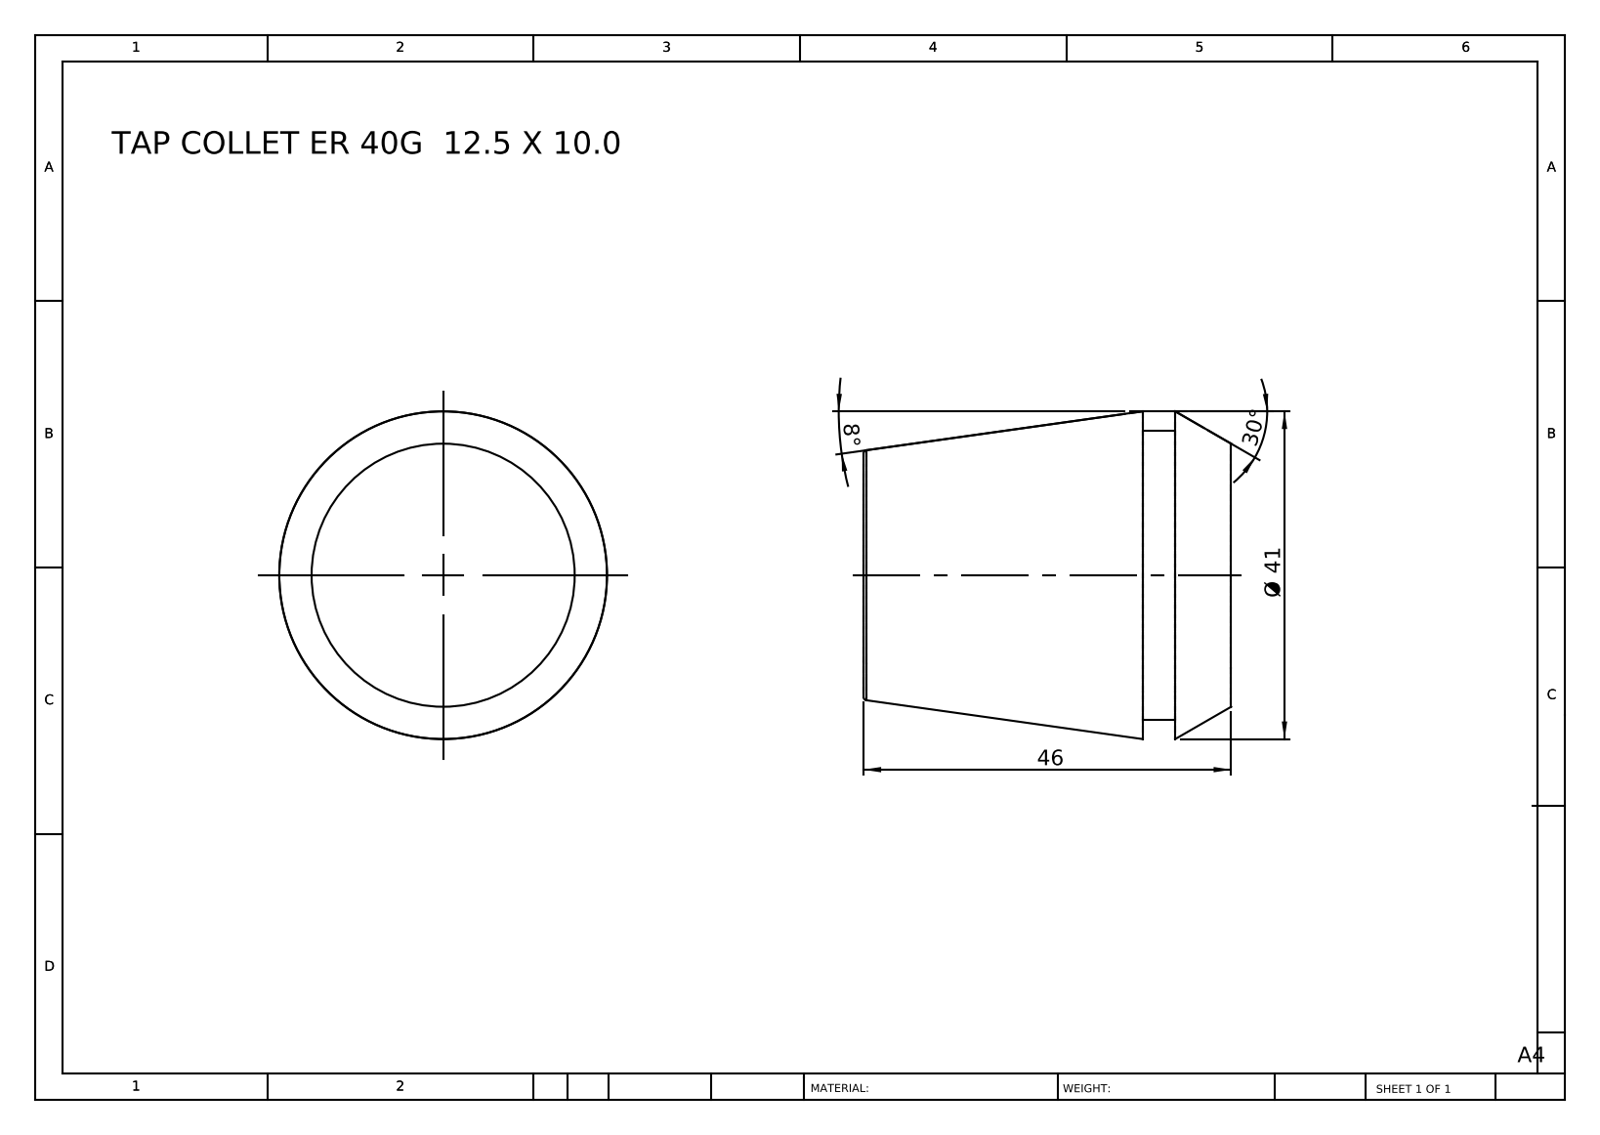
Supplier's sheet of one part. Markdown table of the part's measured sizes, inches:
| quantity | value |
| --- | --- |
| part name | TAP COLLET ER 40G 12.5 X 10.0 |
| STEP written by | SolidWorks 2014 (CONFIG_CONTROL_DESIGN) |
| units | inches |
| bodies | 1 solid, 12 faces (4 planar, 2 cylindrical, 6 other) |
| overall size | 1.811 × 1.614 × 1.614 |
| volume | 2.91 in³ |
| surface area | 11.76 in² |
| round bosses / shafts (diameter × count) | 1.425 × 1 |
| main face-to-face distances | 1.811, 0.437, 1.374, 0.276, 0.161, 1.535 |
